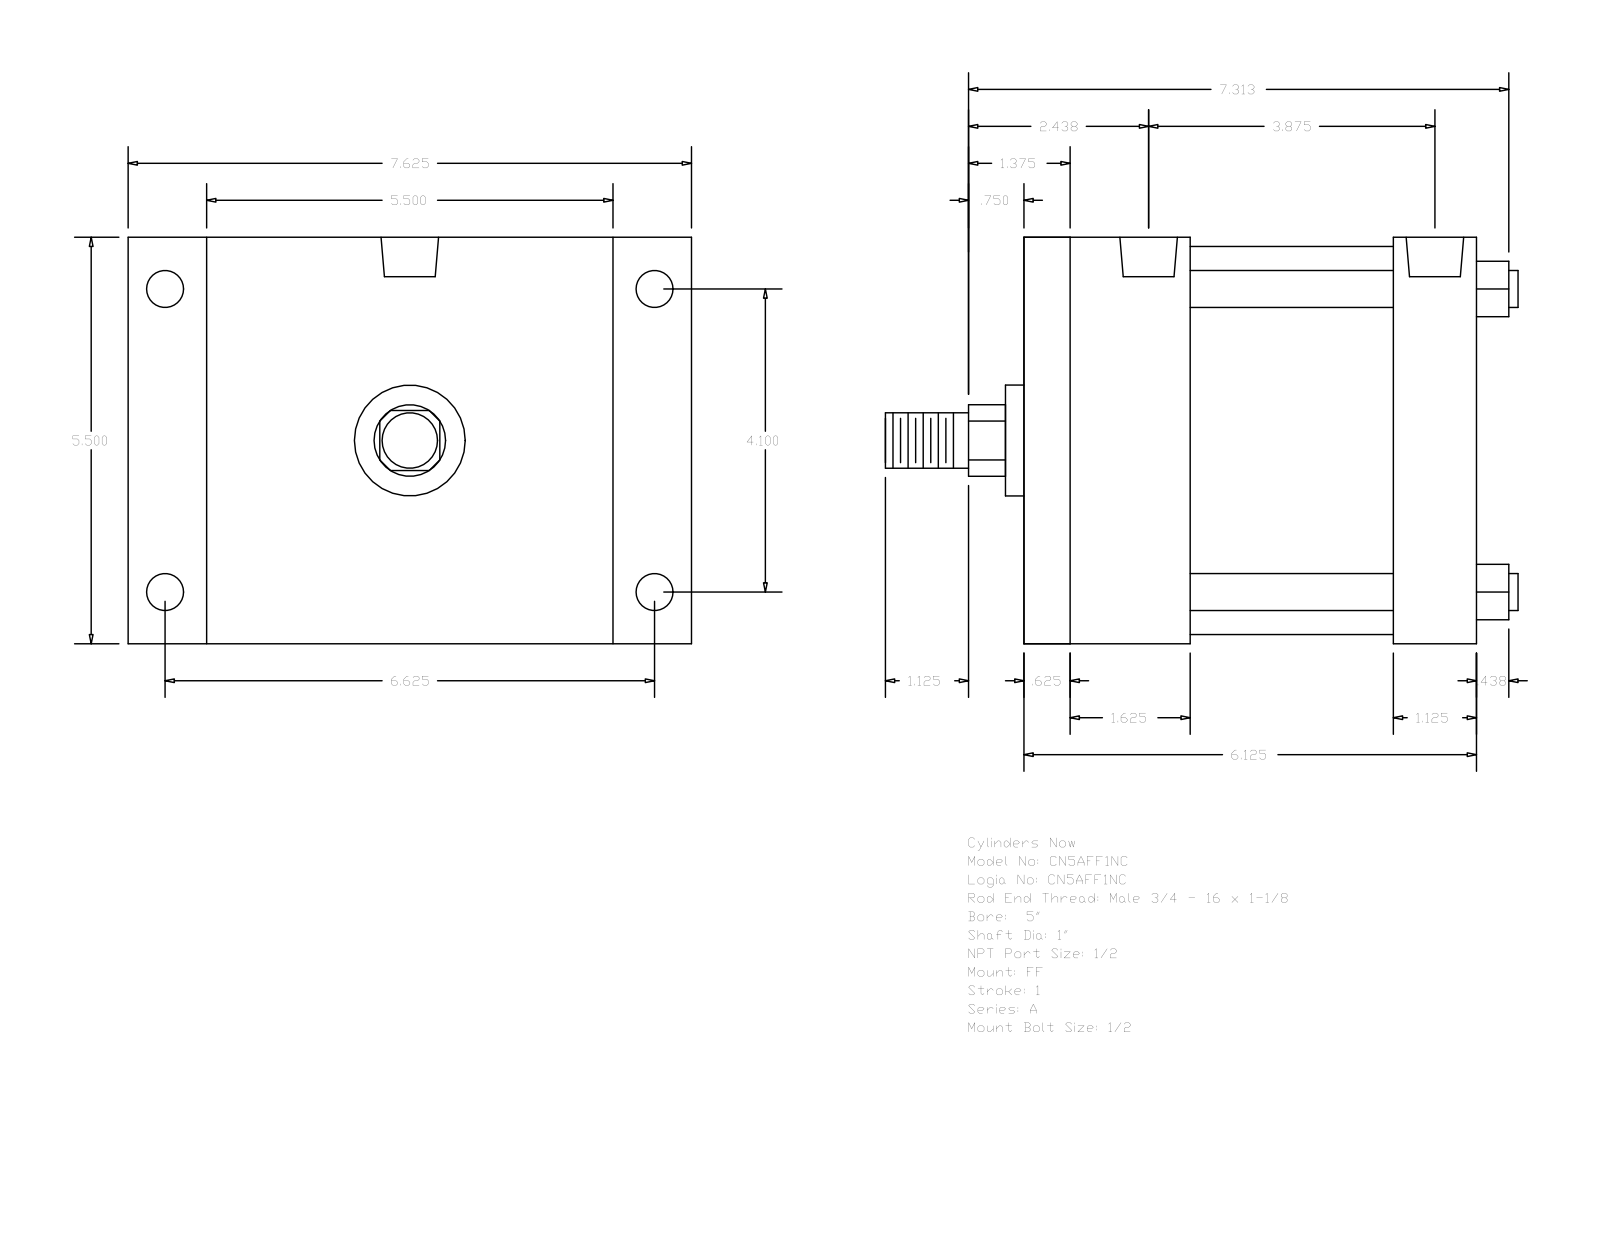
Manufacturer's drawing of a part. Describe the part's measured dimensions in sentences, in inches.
The part is named "A_FF__0500_1". Its 3-D file was written by "GSSL Pune (CONFIG_CONTROL_DESIGN)". It is 0 solids with 92 faces: 64 planar, 28 cylindrical and 0 other. Overall it measures 8.563 by 7.625 by 5.5 inches. Round holes: 4 of diameter 0.344, 4 of diameter 0.5, 2 of diameter 0.778. Round bosses or shafts: 4 of diameter 0.5, 1 of diameter 5.25, 1 of diameter 1.5, 1 of diameter 1, 1 of diameter 0.75. Partial cylindrical surfaces (rounded edges, fillets, slot ends): 1 of radius 0.484. The main face-to-face distances are 5.5, 6.125, 0.625, 6.563, 1.125, 5, 4.375, 2.25, 1.625, 2.75. The hole center spacings are 0.094, 3.687, 3.781, 4.1, 6.625, 7.791, 3.875.
